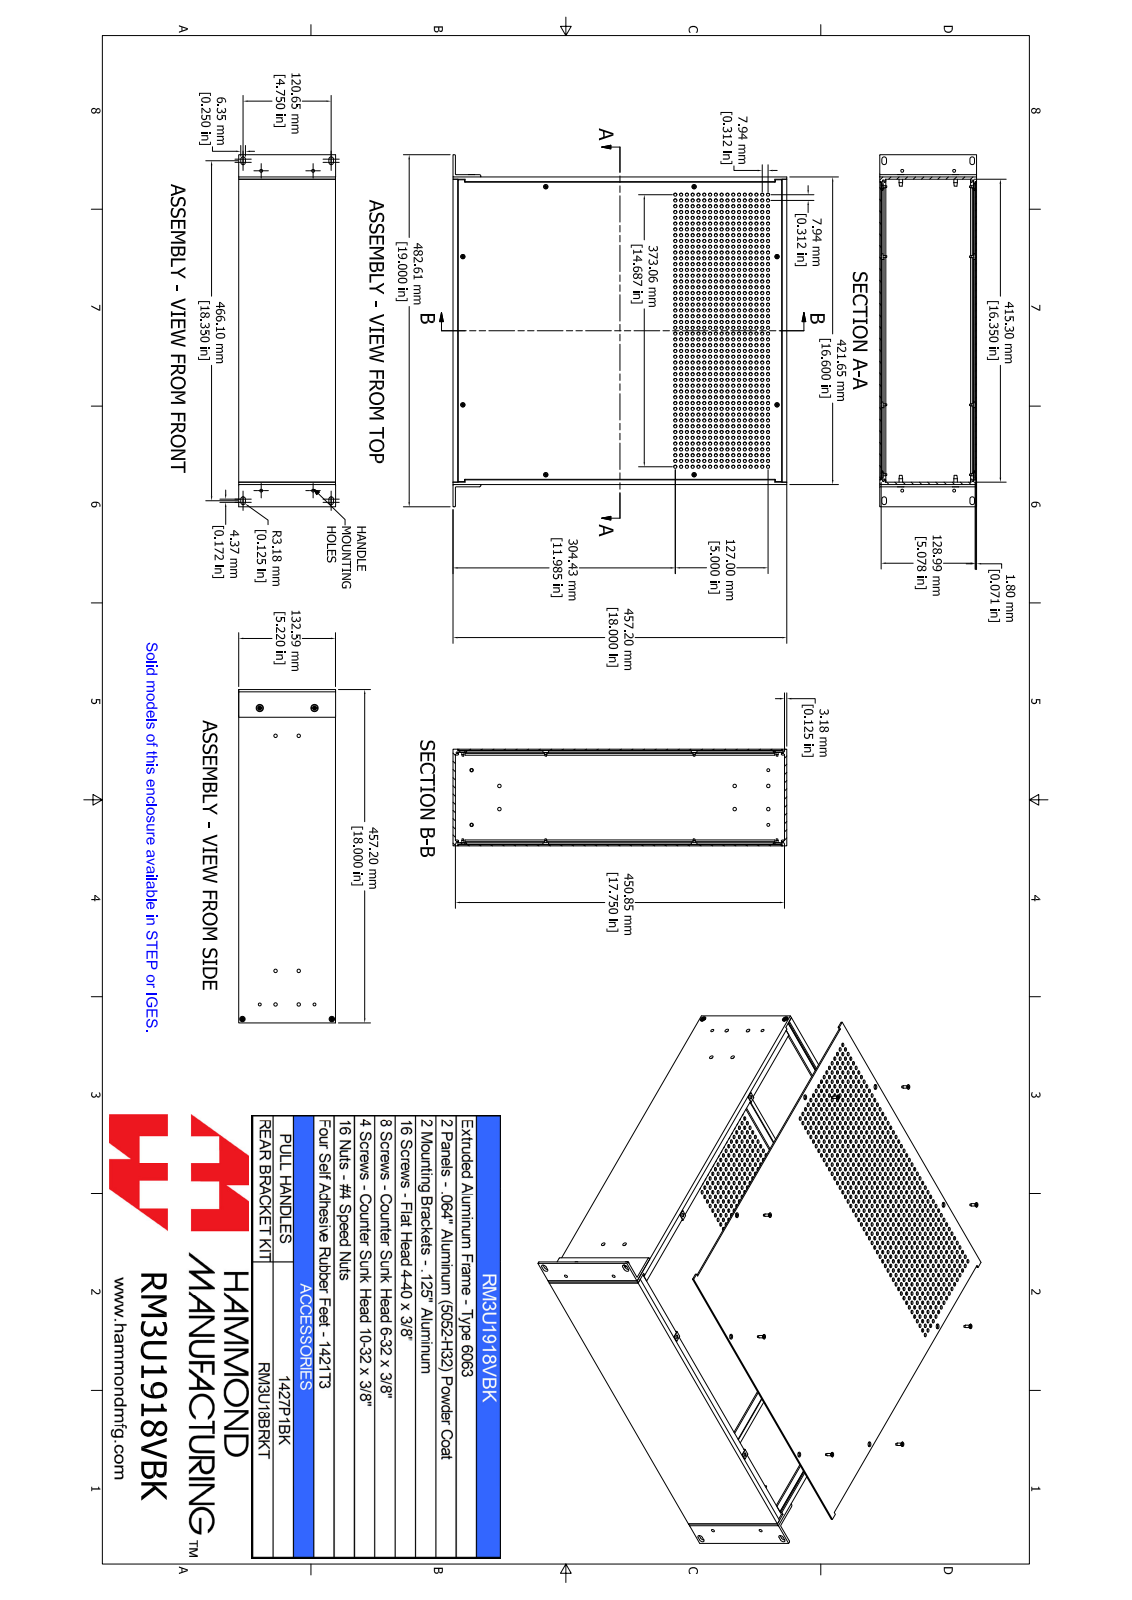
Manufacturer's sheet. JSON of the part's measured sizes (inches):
{"part_name": "RM3U1918VBK", "step_written_by": "SolidWorks 2021 (AUTOMOTIVE_DESIGN)", "units": "inches", "bodies": {"solids": 52, "faces": 2996, "planar": 636, "cylindrical": 1864, "other": 496}, "overall_size": [19, 18, 5.22], "volume_in3": 94.24, "surface_area_in2": 2106, "round_holes": [[0.17, 1632], [0.177, 16], [0.098, 8], [0.157, 8], [0.157, 8], [0.188, 6], [0.159, 4], [0.169, 4], [0.169, 4], [0.197, 2]], "round_bosses_or_shafts": [[0.214, 16], [0.112, 16], [0.238, 4], [0.138, 4], [0.333, 2], [0.19, 2]], "partial_cylinders_radius": [[0.125, 16], [0.039, 14], [0.037, 8], [0.049, 8], [0.05, 8], [0.038, 4], [0.079, 2]], "face_to_face_distances": [0.071, 5.149, 5.22, 5.078, 0.125, 16.476, 0.125, 16.601, 16.35, 18], "hole_center_spacings": [1.25, 0.313, 0.937, 1.563, 8, 0.625, 2.5, 13.031]}
